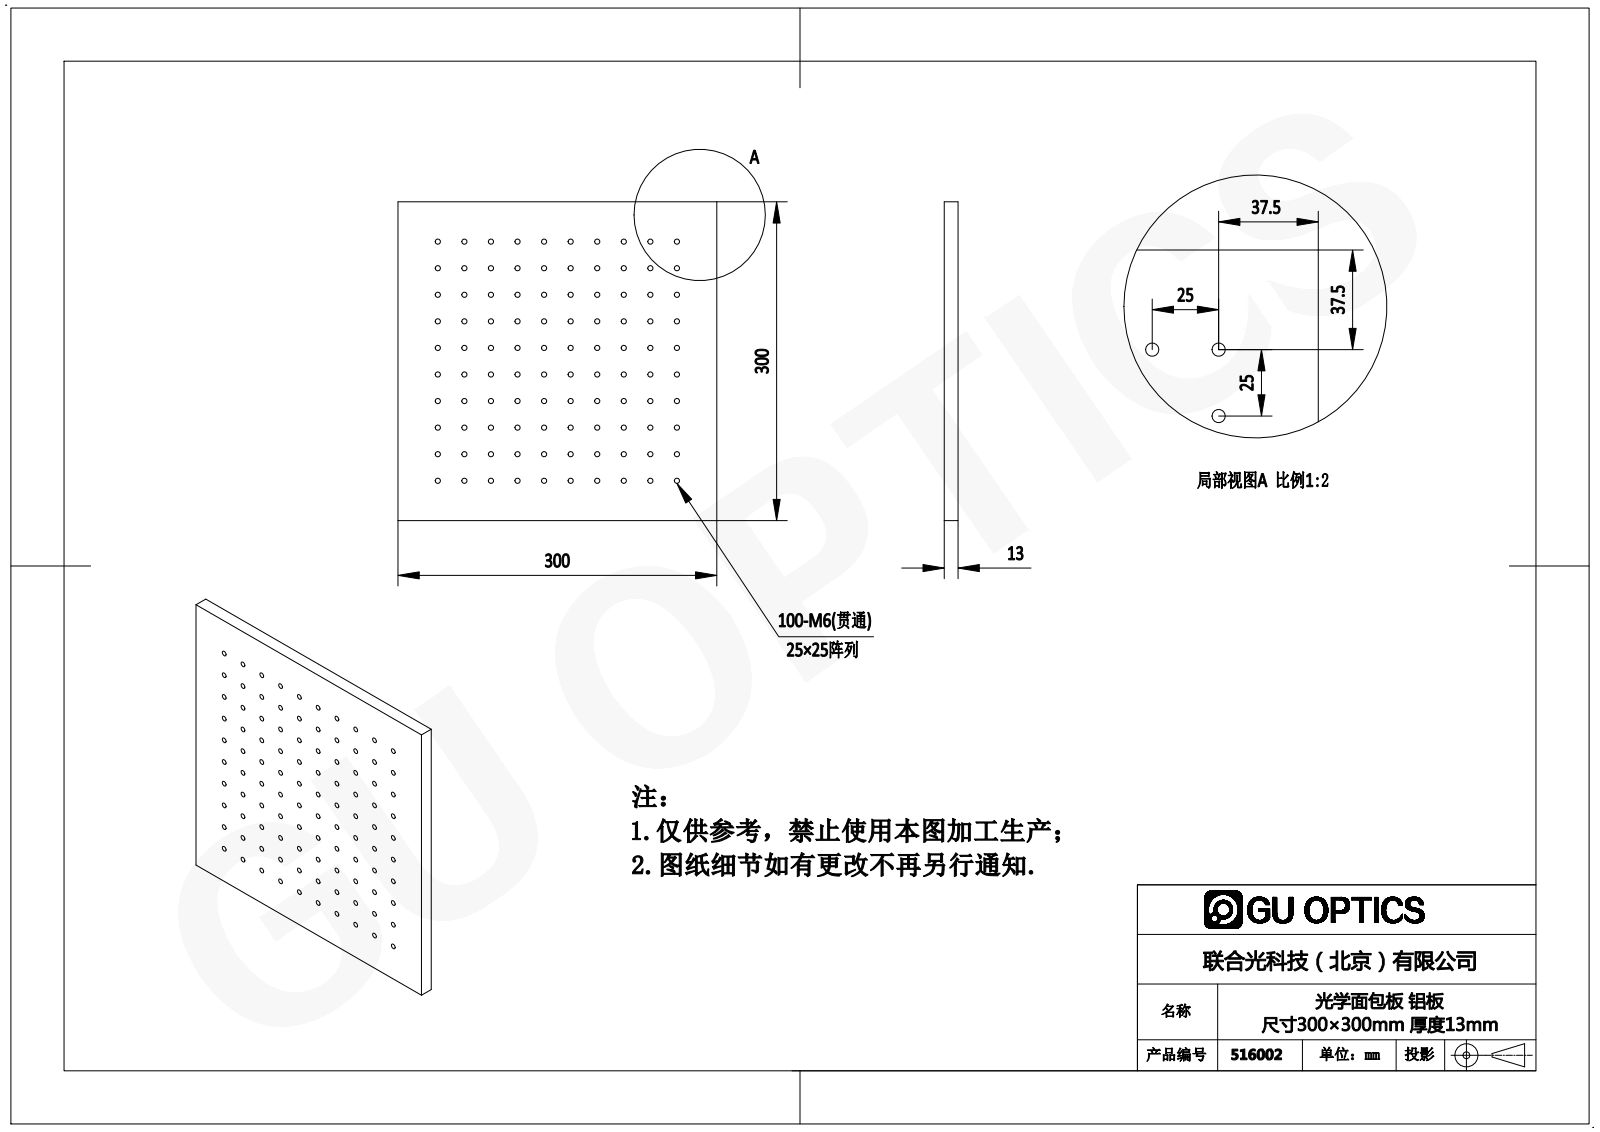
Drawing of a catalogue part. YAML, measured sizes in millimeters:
part_name: "516002"
step_written_by: "SolidWorks 2020 (CONFIG_CONTROL_DESIGN)"
units: millimeters
bodies: {solids: 1, faces: 139, planar: 10, cylindrical: 129, other: 0}
overall_size: [300, 300, 13]
volume: 1136000
surface_area: 216718
round_holes:
  - {diameter: 5, count: 121}
  - {diameter: 5.8, count: 4}
  - {diameter: 11, count: 4}
face_to_face_distances: [13, 300, 6.5]
hole_center_spacings: [25, 50, 75, 35.36, 55.9, 125, 100, 79.06]
